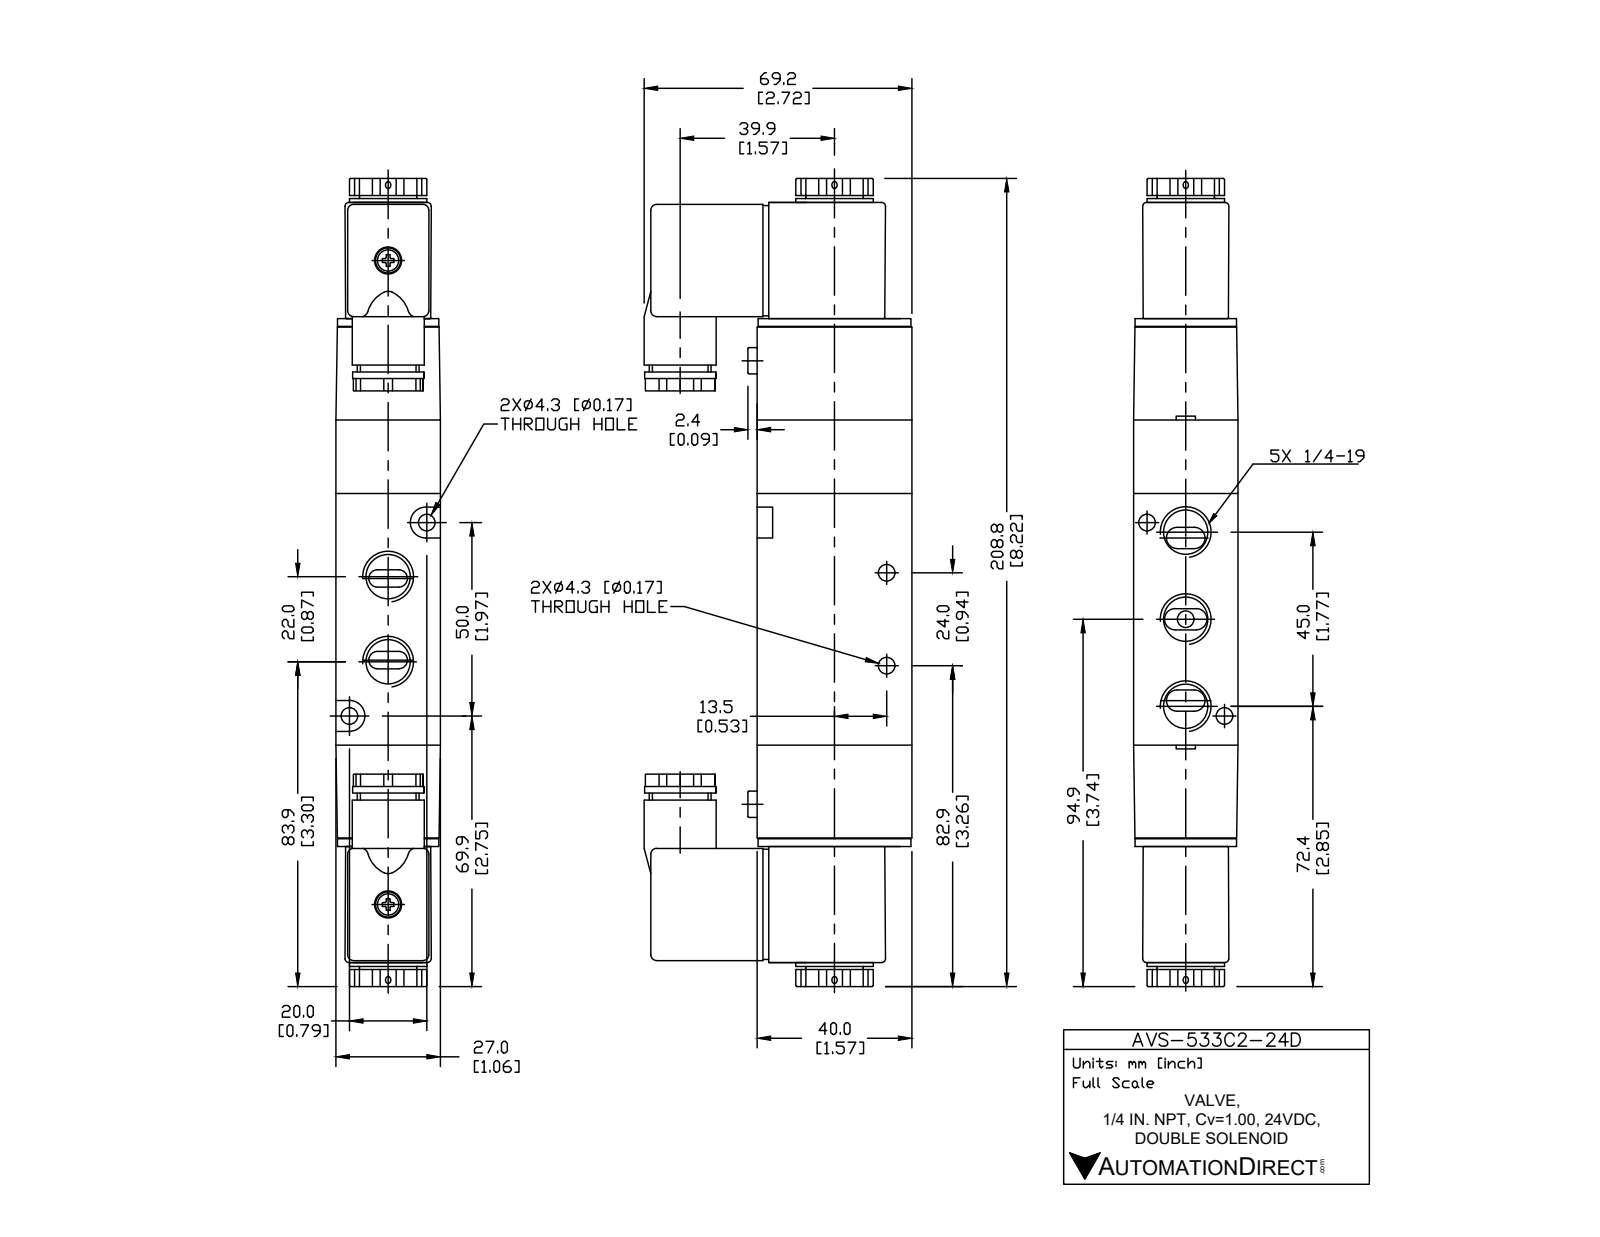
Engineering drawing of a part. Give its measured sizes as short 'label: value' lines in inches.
name: AVS-533C2-24D
written by: SolidWorks 2015 (CONFIG_CONTROL_DESIGN)
unit: in
bodies: 5 solids, 278 faces (133 planar, 111 cylindrical, 34 other)
size: 8.22 × 2.724 × 1.063
volume: 13.7 in³; area: 70.72 in²
holes: 5× ⌀0.438, 4× ⌀0.169, 1× ⌀0.366
bosses: 2× ⌀0.264, 1× ⌀0.787, 1× ⌀0.732, 1× ⌀0.724, 1× ⌀0.63, 1× ⌀0.583
rounds: 18× R0.059, 12× R0.118, 10× R0.039, 8× R0.02
face distances: 1.063, 0.118, 0.945, 1.575, 3.307, 0.914, 0.827, 1.161, 0.02, 6.551
hole spacings: 0.406, 0.433, 0.453, 0.677, 0.886, 1.06, 1.319, 1.471
